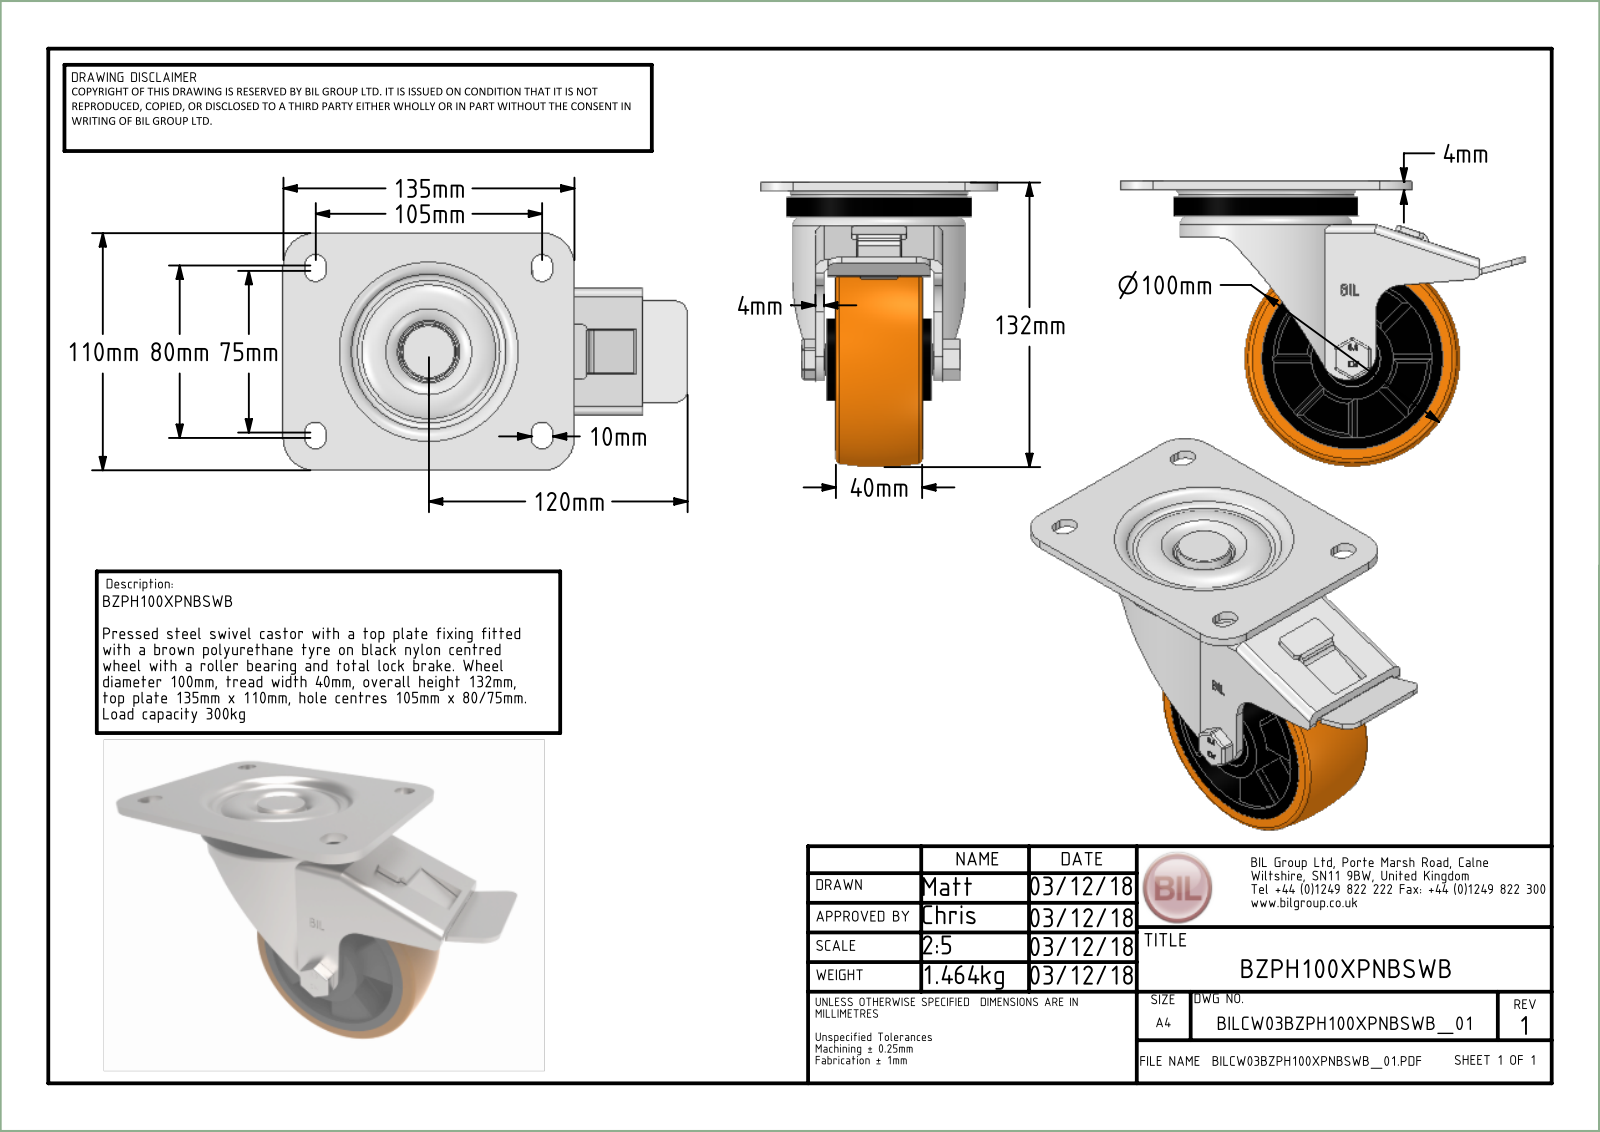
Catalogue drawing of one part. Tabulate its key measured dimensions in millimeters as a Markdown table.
| quantity | value |
| --- | --- |
| part name | BZPH100XPNBSWB v3; BZPH100ASSWB v1; ZINC PLATED, PRESSED STEEL TOP PLATE; ZINC PLATED, PRESSED STEEL FORKS (+8 more) |
| STEP written by | Autodesk Translation Framework v14.10.0.0 (AUTOMOTIVE_DESIGN) |
| units | millimeters |
| bodies | 23 solids, 923 faces (446 planar, 209 cylindrical, 268 other) |
| overall size | 187.5 × 132 × 110 |
| volume | 399 187 mm³ |
| surface area | 182 796 mm² |
| round holes (diameter × count) | 26 × 2, 8 × 1, 10 × 1, 10.2 × 1, 10.5 × 1, 12 × 1, 15 × 1, 15.5 × 1, 27 × 1, 28 × 1, 72 × 1, 73 × 1 |
| round bosses / shafts (diameter × count) | 4 × 8, 83.5 × 1, 80 × 1, 60 × 1, 51 × 1, 37 × 1, 32 × 1, 26.9 × 1 |
| partial cylindrical surfaces (radius × count) | 0.5 × 27, 2 × 15, 0.75 × 10, 4 × 10, 5.5 × 8, 1.5 × 7, 1.25 × 4, 3 × 4 |
| main face-to-face distances | 4, 9, 13, 9.5, 5, 1, 5.5, 49.5, 55, 45.5 |
